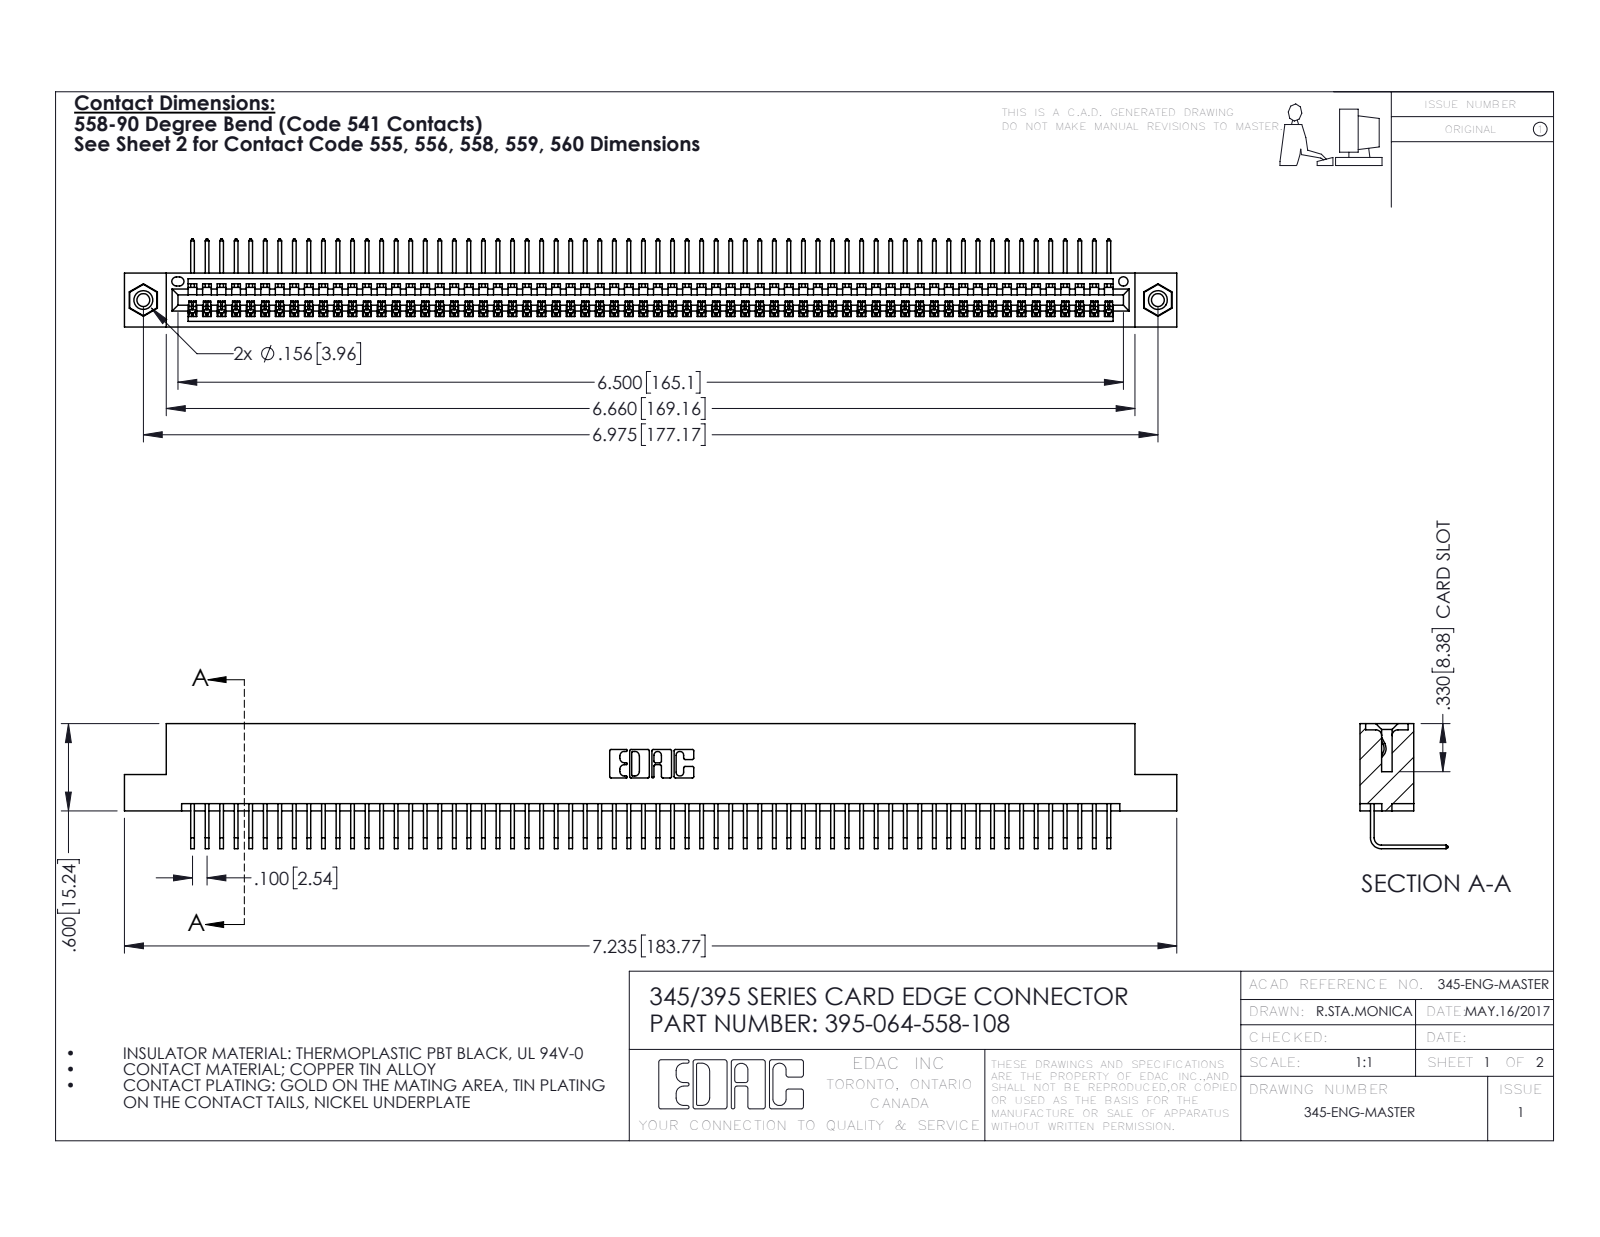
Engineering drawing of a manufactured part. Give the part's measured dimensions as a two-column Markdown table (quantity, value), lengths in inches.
| quantity | value |
| --- | --- |
| part name | 345-250-001_345-250-003-102; 345-292-001_558 Tail - 2; 395-064-558-108; 345 Part_Flush Mounting Lugs - 0.156 Dia-TI |
| STEP written by | SolidWorks 2016 (CONFIG_CONTROL_DESIGN) |
| units | inches |
| bodies | 67 solids, 4026 faces (2800 planar, 1210 cylindrical, 16 other) |
| overall size | 7.235 × 0.859 × 0.605 |
| volume | 1.089 in³ |
| surface area | 39.19 in² |
| round holes (diameter × count) | 0.089 × 2, 0.125 × 2, 0.156 × 2, 0.064 × 1 |
| round bosses / shafts (diameter × count) | 0.155 × 2 |
| partial cylindrical surfaces (radius × count) | 0.006 × 128, 0.01 × 22, 0.007 × 6, 0.031 × 6, 0.026 × 3, 0.031 × 2, 0.04 × 2, 0.014 × 1 |
| main face-to-face distances | 0.072, 0.298, 0.37, 0.2, 0.098, 0.272, 0.025, 0.225, 0.149, 0.072 |
| hole center spacings | 0.27, 6.739, 6.975 |
